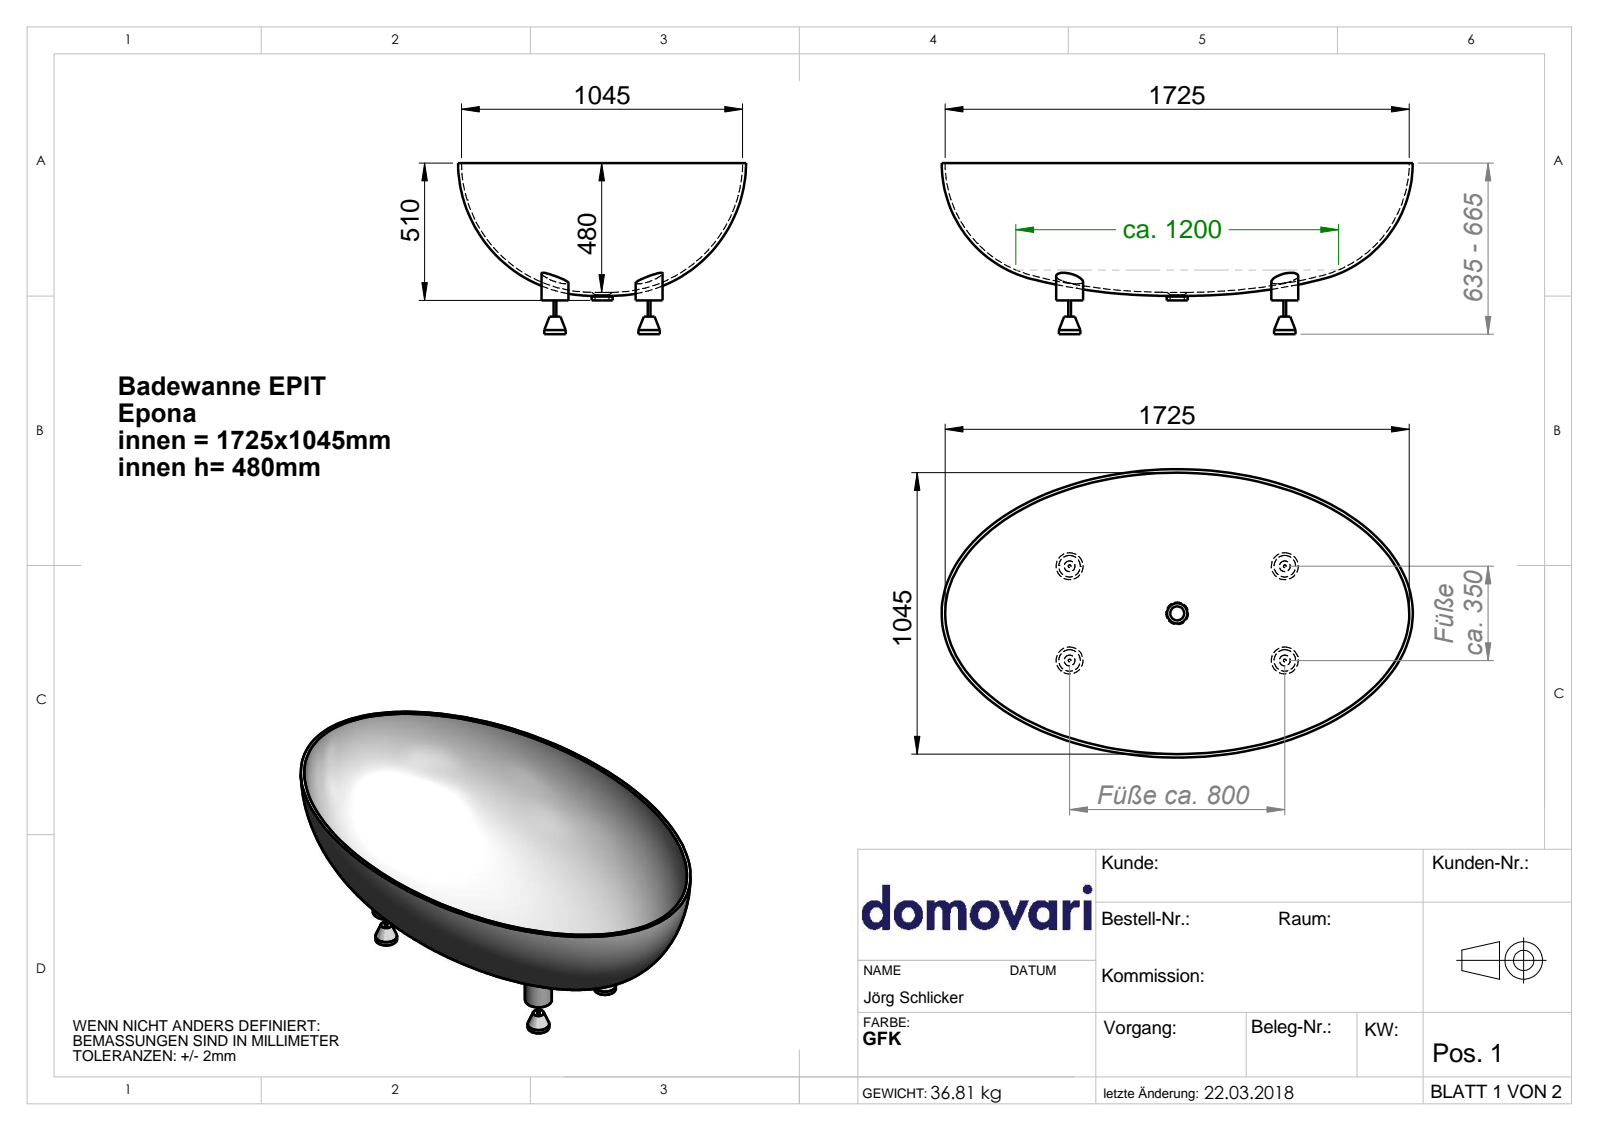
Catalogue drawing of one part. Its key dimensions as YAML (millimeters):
part_name: "EPIT"
step_written_by: "SolidWorks 2017 (AUTOMOTIVE_DESIGN)"
units: millimeters
bodies: {solids: 2, faces: 68, planar: 24, cylindrical: 24, other: 20}
overall_size: [1751, 1071, 635]
volume: 36850000
surface_area: 5525000
round_bosses_or_shafts:
  - {diameter: 100, count: 4}
  - {diameter: 80, count: 4}
  - {diameter: 10, count: 4}
face_to_face_distances: [10, 1055, 500, 510, 1735, 125, 625, 635, 1065, 1045]
